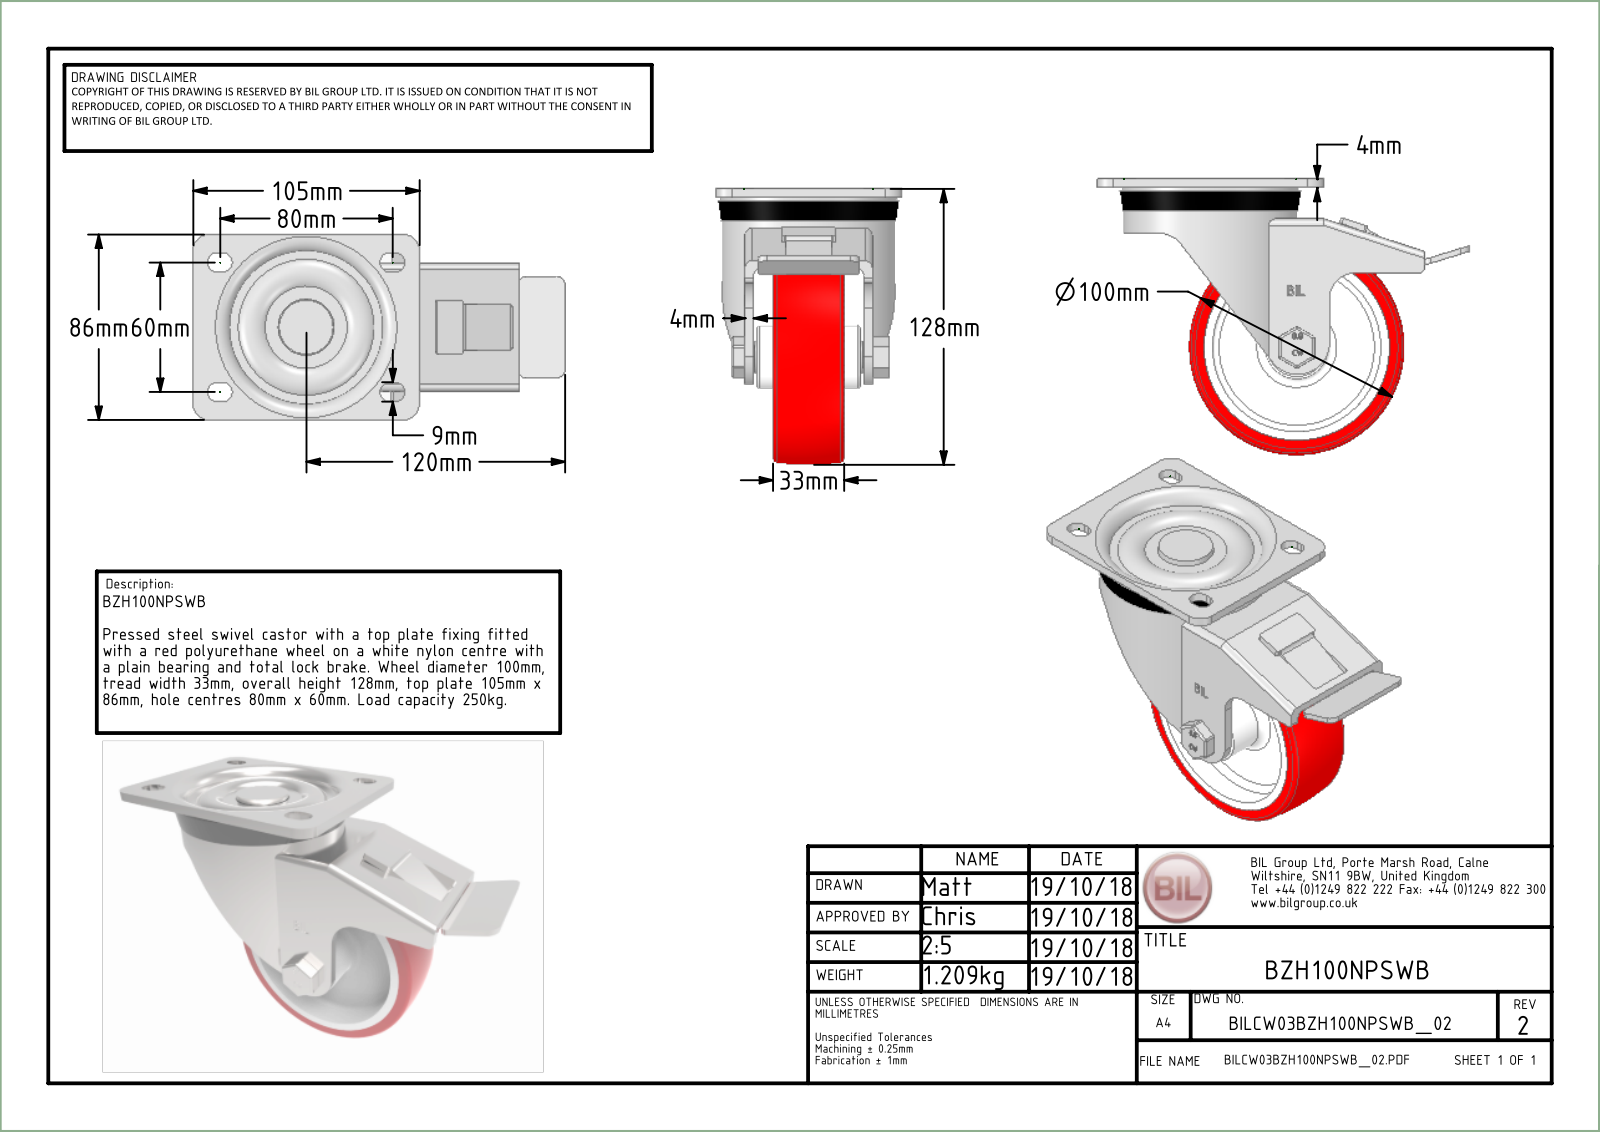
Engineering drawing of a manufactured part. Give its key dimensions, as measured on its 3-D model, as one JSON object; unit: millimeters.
{"part_name": "BZH100NPSWB v3; BZH100ASSWB v1; ZINC PLATED, PRESSED STEEL TOP PLATE; ZINC PLATED, PRESSED STEEL FORKS (+8 more)", "step_written_by": "Autodesk Translation Framework v14.10.0.0 (AUTOMOTIVE_DESIGN)", "units": "millimeters", "bodies": {"solids": 12, "faces": 606, "planar": 316, "cylindrical": 194, "other": 96}, "overall_size": [172.5, 128, 86], "volume_mm3": 324977, "surface_area_mm2": 145737, "round_holes": [[6, 1], [10, 1], [10.2, 1], [10.5, 1], [12, 1], [15.4, 1], [25, 1], [32, 1], [72, 1], [82, 1]], "round_bosses_or_shafts": [[80, 1], [60, 1], [31, 1], [30, 1], [20, 1], [16, 1], [15, 1], [9.85, 1]], "partial_cylinders_radius": [[0.5, 27], [2, 18], [4, 10], [4.5, 8], [0.75, 6], [1.5, 6], [8, 4], [1, 3]], "face_to_face_distances": [4, 19, 14, 23, 9, 7.5, 5, 13, 1, 27]}
